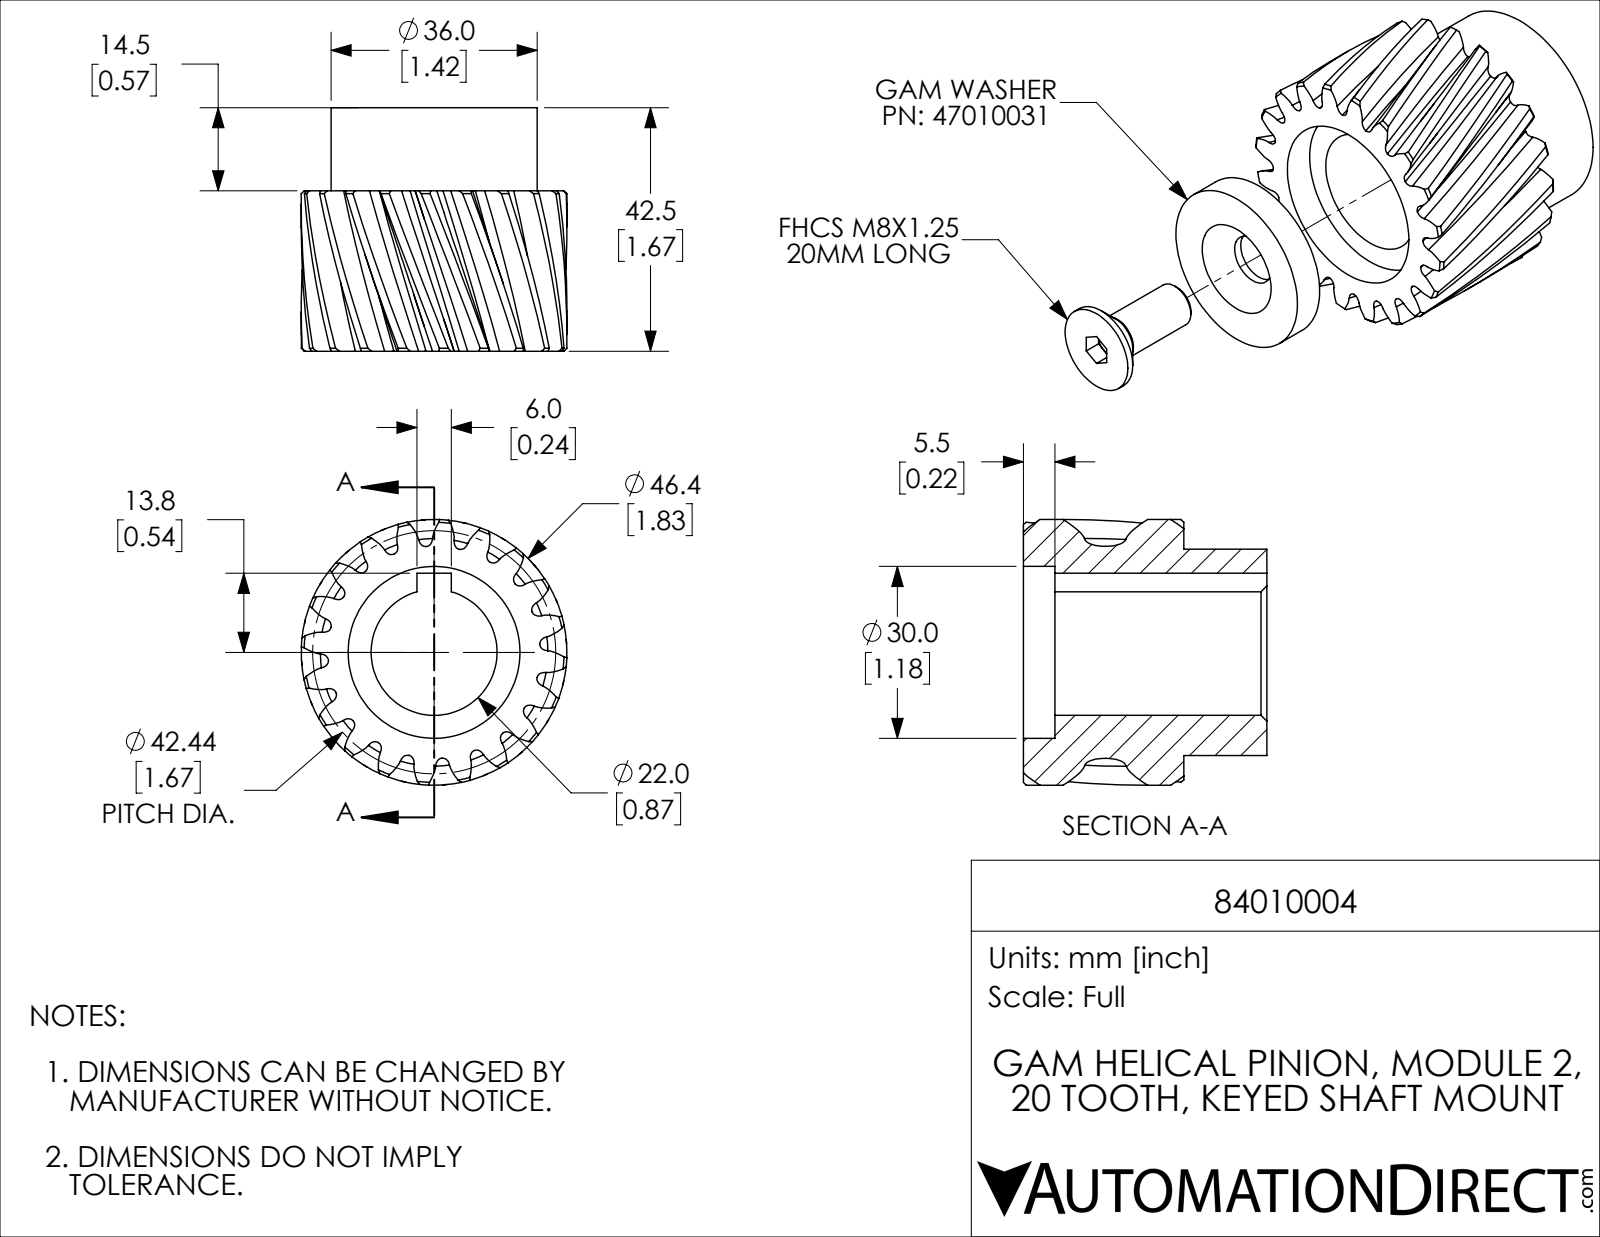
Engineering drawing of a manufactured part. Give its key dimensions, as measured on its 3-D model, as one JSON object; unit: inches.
{"part_name": "84010004", "step_written_by": "SolidWorks 2019 (CONFIG_CONTROL_DESIGN)", "units": "inches", "bodies": {"solids": 3, "faces": 193, "planar": 23, "cylindrical": 37, "other": 133}, "overall_size": [1.827, 1.827, 1.673], "volume_in3": 2.414, "surface_area_in2": 26.53, "round_holes": [[0.354, 1], [0.866, 1], [1.181, 1]], "round_bosses_or_shafts": [[1.827, 1], [1.417, 1], [0.61, 1], [0.315, 1]], "face_to_face_distances": [0.217, 1.673, 1.457, 0.571, 0.886, 1.102, 0.236, 0.787, 0.315, 0.197]}
